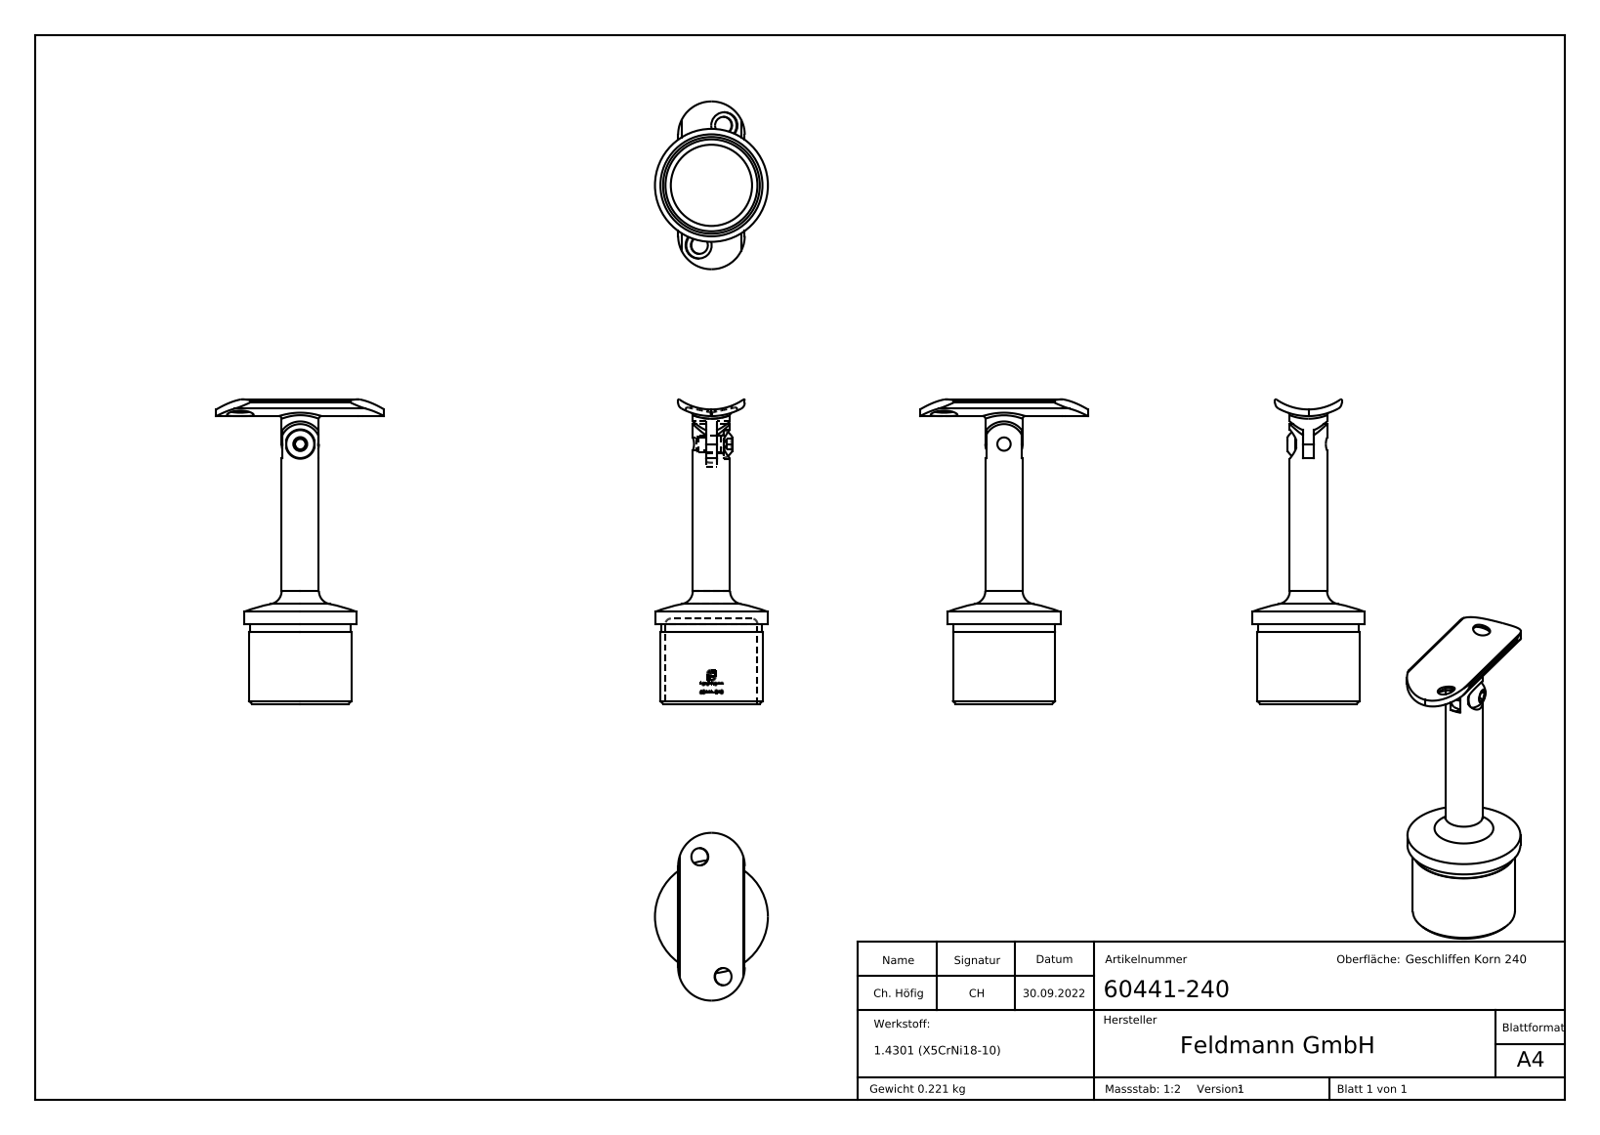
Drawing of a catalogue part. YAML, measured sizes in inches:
part_name: "60441-240; 6044x-XXX Teil1_60441-240 Teil1; DIN 7380_DIN 7380 M6x10; 6044x-XXX Teil2_60441-240 Teil2"
step_written_by: "SolidWorks 2018 (CONFIG_CONTROL_DESIGN)"
units: inches
bodies: {solids: 3, faces: 335, planar: 159, cylindrical: 59, other: 117}
overall_size: [4.5, 2.48, 1.669]
volume: 1.706
surface_area: 28.01
round_holes:
  - {diameter: 0.256, count: 3}
  - {diameter: 0.394, count: 2}
  - {diameter: 0.197, count: 1}
  - {diameter: 0.433, count: 1}
  - {diameter: 1.358, count: 1}
round_bosses_or_shafts:
  - {diameter: 1.669, count: 1}
  - {diameter: 1.508, count: 1}
  - {diameter: 1.492, count: 1}
  - {diameter: 0.551, count: 1}
  - {diameter: 0.413, count: 1}
  - {diameter: 0.236, count: 1}
partial_cylinders:
  - {radius: 0.012, count: 2}
  - {radius: 0.098, count: 2}
  - {radius: 0.492, count: 2}
  - {radius: 0.295, count: 1}
  - {radius: 0.335, count: 1}
  - {radius: 0.683, count: 1}
  - {radius: 0.835, count: 1}
  - {radius: 0.933, count: 1}
face_to_face_distances: [0.079, 0.156, 0.157, 0.154, 1.181, 1.26, 0.1, 0.256, 0.254, 0.098]
